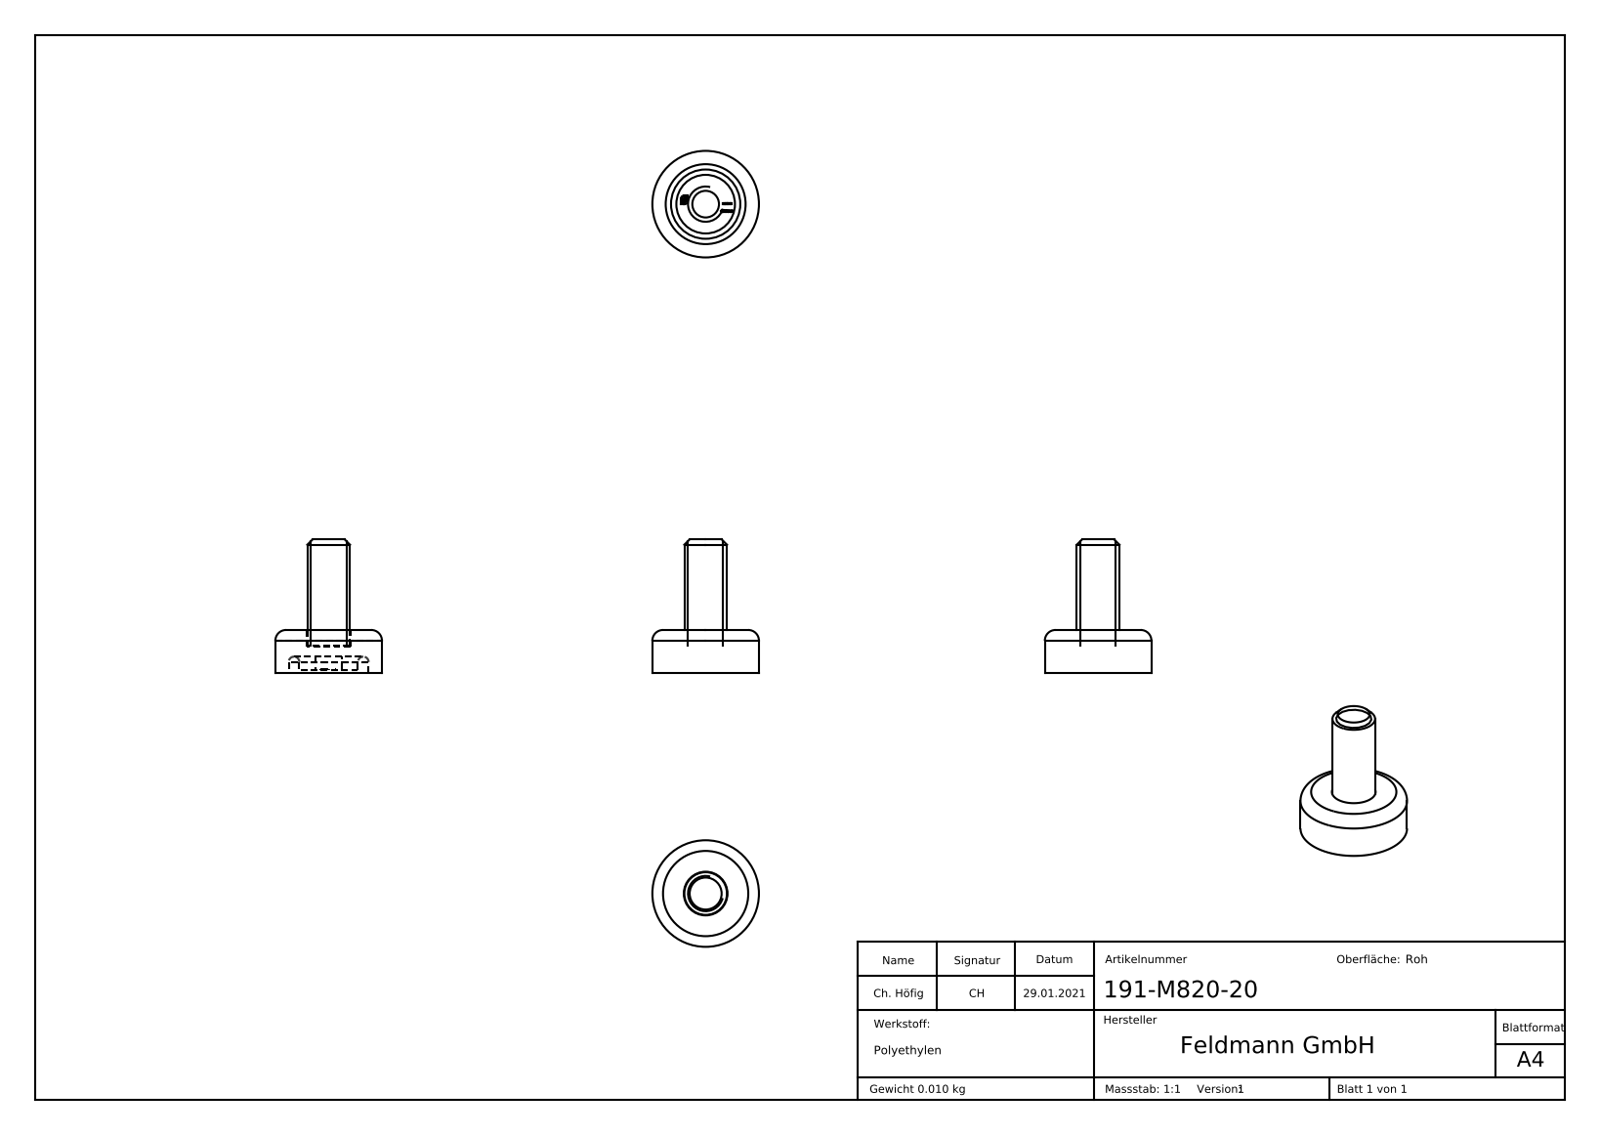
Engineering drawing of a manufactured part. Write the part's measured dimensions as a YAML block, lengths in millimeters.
part_name: "191-M820-20"
step_written_by: "SolidWorks 2018 (CONFIG_CONTROL_DESIGN)"
units: millimeters
bodies: {solids: 2, faces: 301, planar: 157, cylindrical: 12, other: 132}
overall_size: [25, 20, 20]
volume: 2968
surface_area: 1978
round_holes:
  - {diameter: 5, count: 1}
  - {diameter: 8.2, count: 1}
  - {diameter: 15, count: 1}
round_bosses_or_shafts:
  - {diameter: 20, count: 1}
  - {diameter: 11, count: 1}
  - {diameter: 8, count: 1}
face_to_face_distances: [8, 7.5, 0.5, 3, 5, 4.4, 4.9, 3.1, 4.5, 25]
